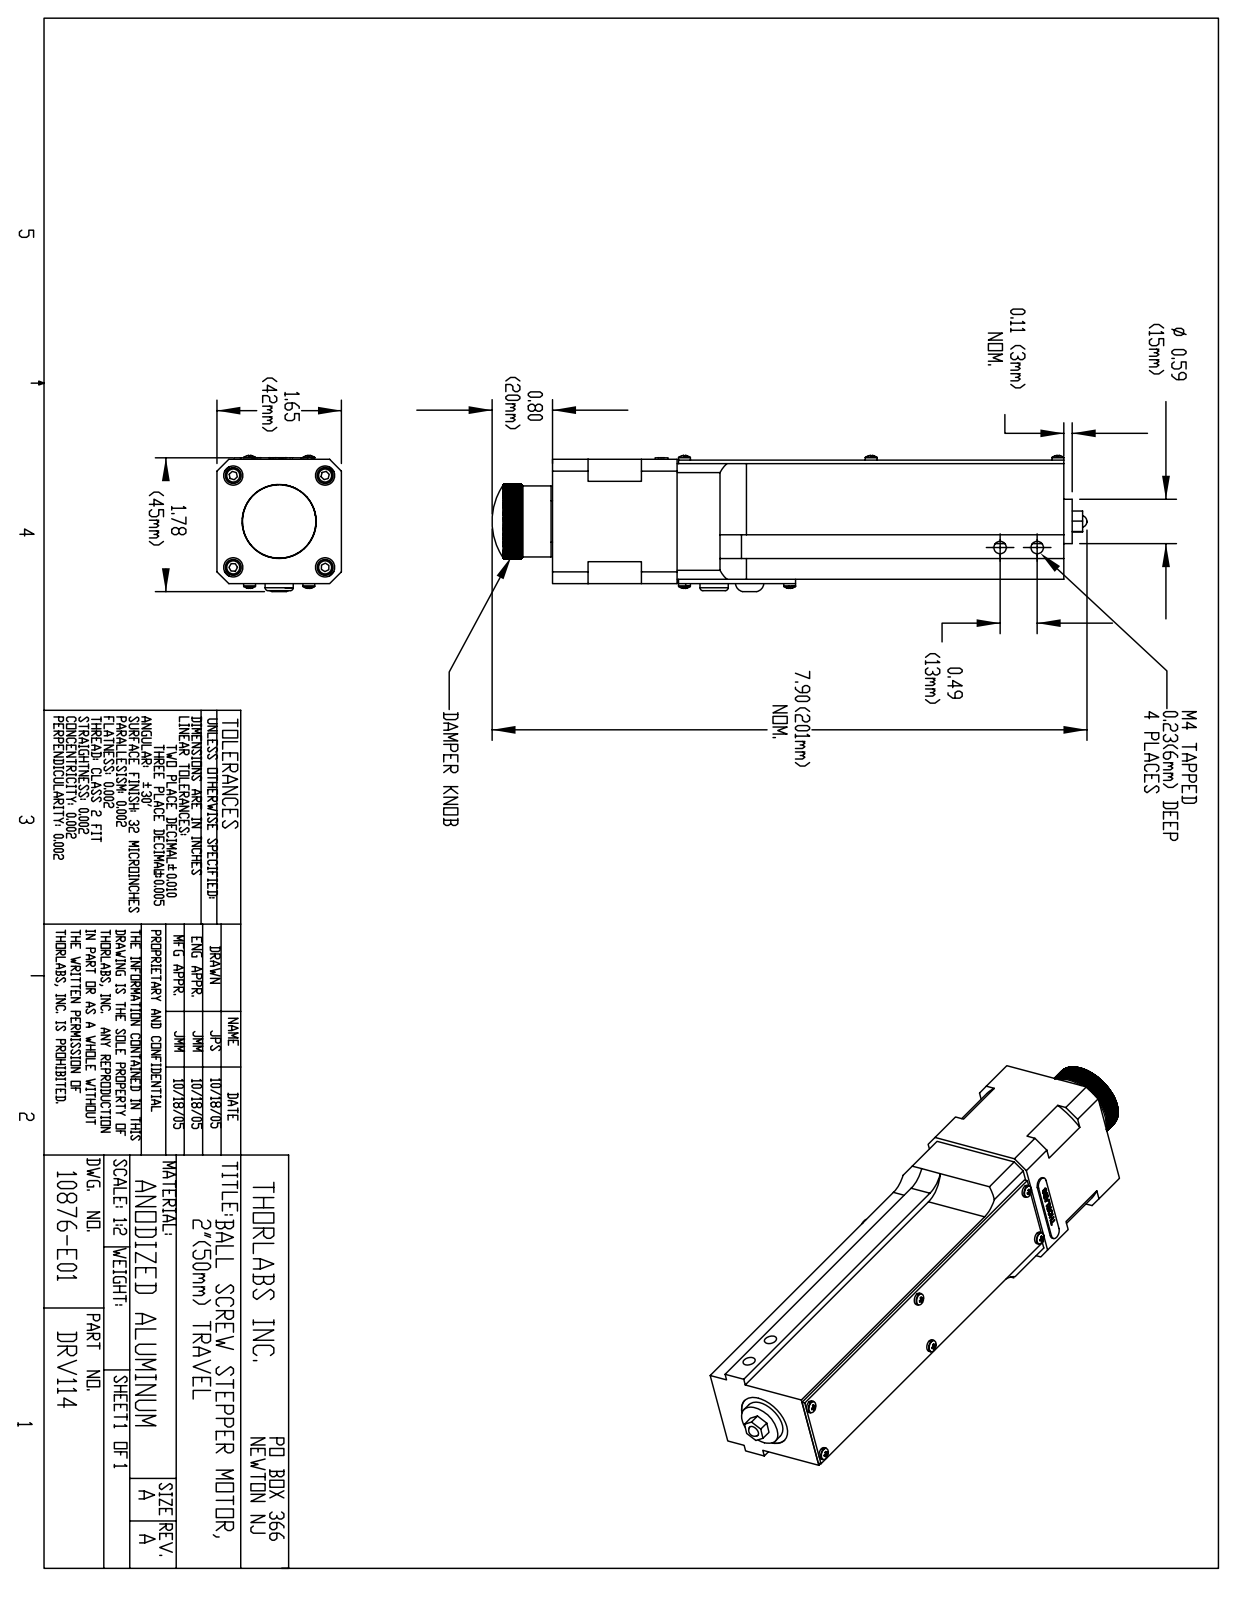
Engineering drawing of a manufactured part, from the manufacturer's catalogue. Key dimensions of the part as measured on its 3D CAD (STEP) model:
Part name (STEP PRODUCT): 10876-E0W
STEP written by: SolidWorks 2007 (AUTOMOTIVE_DESIGN)
Units: inches
Bodies: 0 solids, 1009 faces (734 planar, 209 cylindrical, 66 other)
Overall size (bounding box): 7.902 × 1.81 × 1.654
Round holes (diameter × count): ⌀0.256 ×4, ⌀0.165 ×2, ⌀0.098 ×1, ⌀0.156 ×1, ⌀0.189 ×1, ⌀0.748 ×1
Round bosses / shafts (diameter × count): ⌀0.157 ×8, ⌀0.945 ×1, ⌀0.591 ×1, ⌀0.375 ×1
Partial cylindrical surfaces — rounded edges, fillets, slot ends (radius × count): R0.394 ×4, R0.087 ×2, R0.492 ×1, R0.984 ×1
Main face-to-face distances: 0.059, 1.654, 1.102, 1.594, 0.276, 1.583, 1.378, 1.642, 0.181, 1.472
Hole centre spacings: 0.863, 1.22, 1.726, 0.472, 0.492
